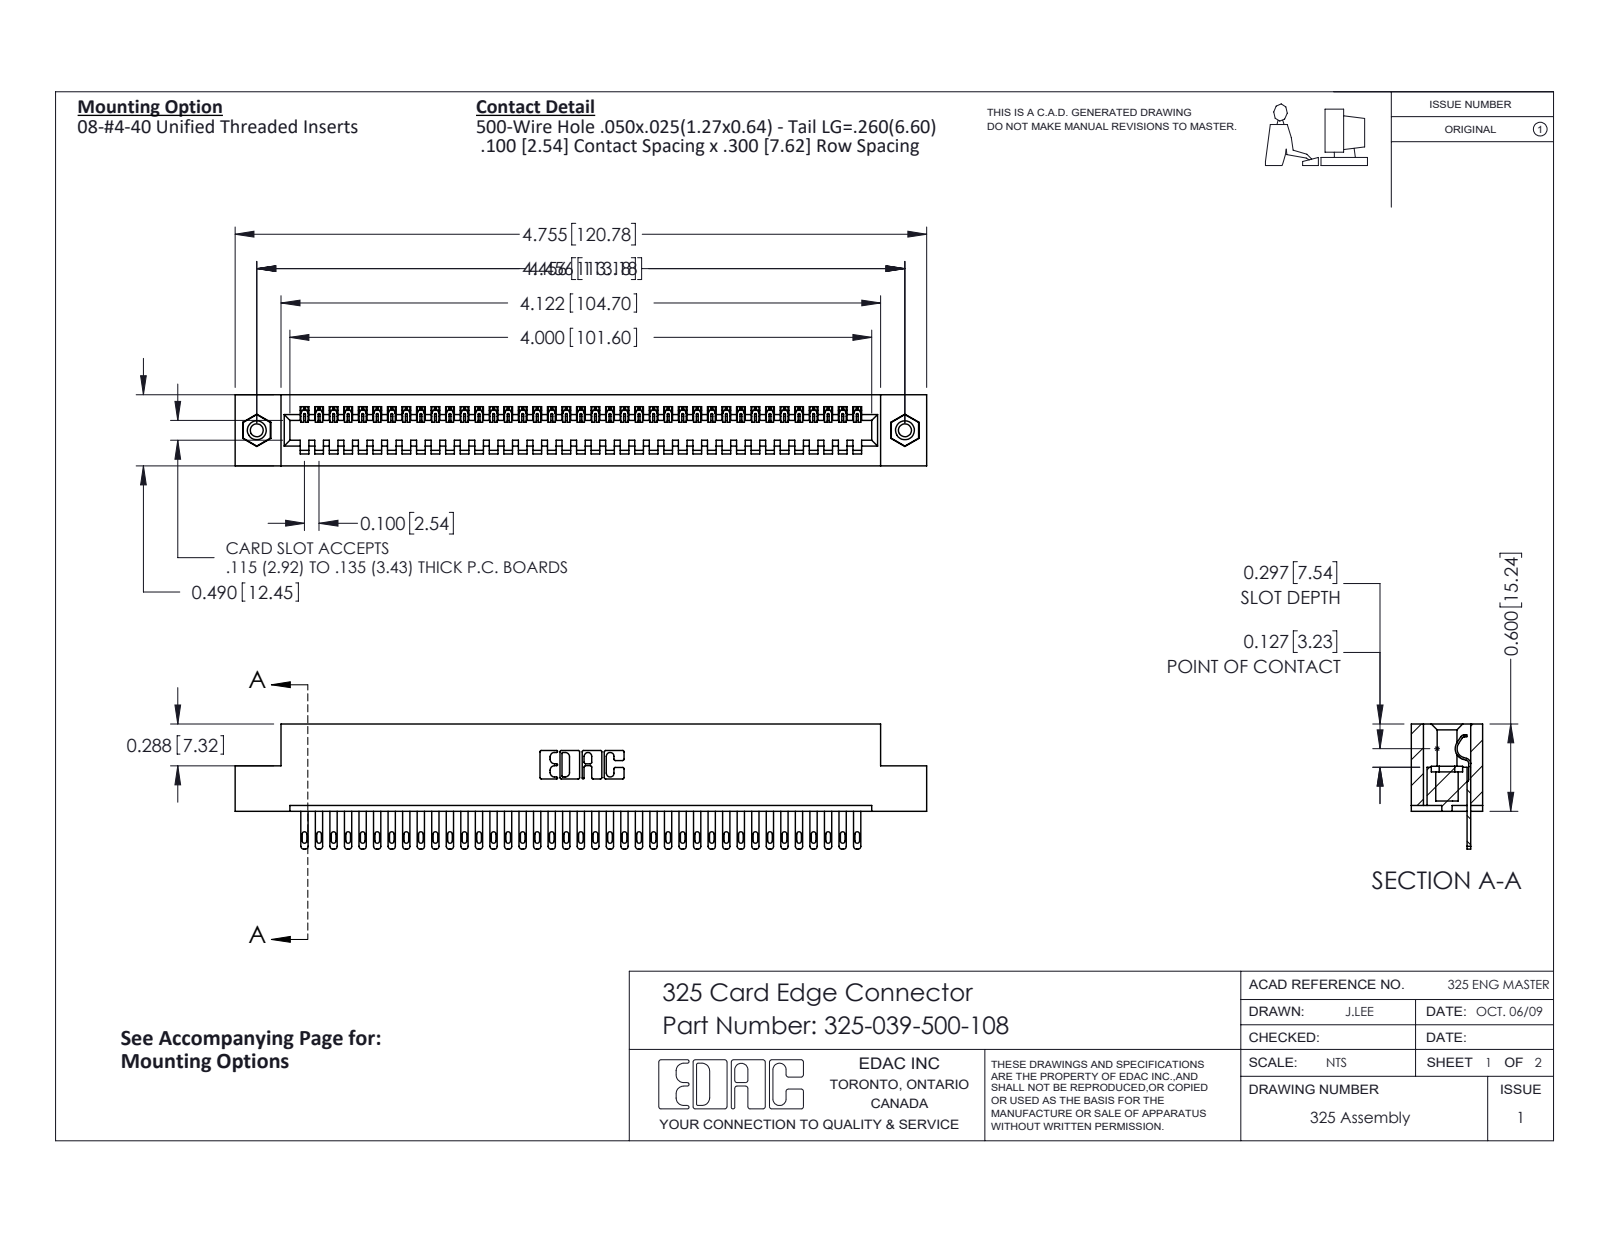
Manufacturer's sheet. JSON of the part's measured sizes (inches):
{"part_name": "325-039-500-108; 325 Part_TI; 345-250-001_345-250-003-102; 325-292-001_325-293-100", "step_written_by": "SolidWorks 2016 (CONFIG_CONTROL_DESIGN)", "units": "inches", "bodies": {"solids": 42, "faces": 2280, "planar": 1506, "cylindrical": 758, "other": 16}, "overall_size": [4.755, 0.86, 0.49], "volume_in3": 0.935, "surface_area_in2": 26.04, "round_holes": [[0.089, 2], [0.125, 2], [0.16, 2]], "round_bosses_or_shafts": [[0.155, 2]], "partial_cylinders_radius": [[0.006, 78], [0.016, 78], [0.02, 78], [0.01, 22], [0.007, 6], [0.031, 6], [0.026, 3], [0.014, 1]], "face_to_face_distances": [0.083, 0.407, 0.49, 0.3, 0.107, 0.383, 0.025, 0.325, 0.56, 0.04], "hole_center_spacings": [4.456]}
